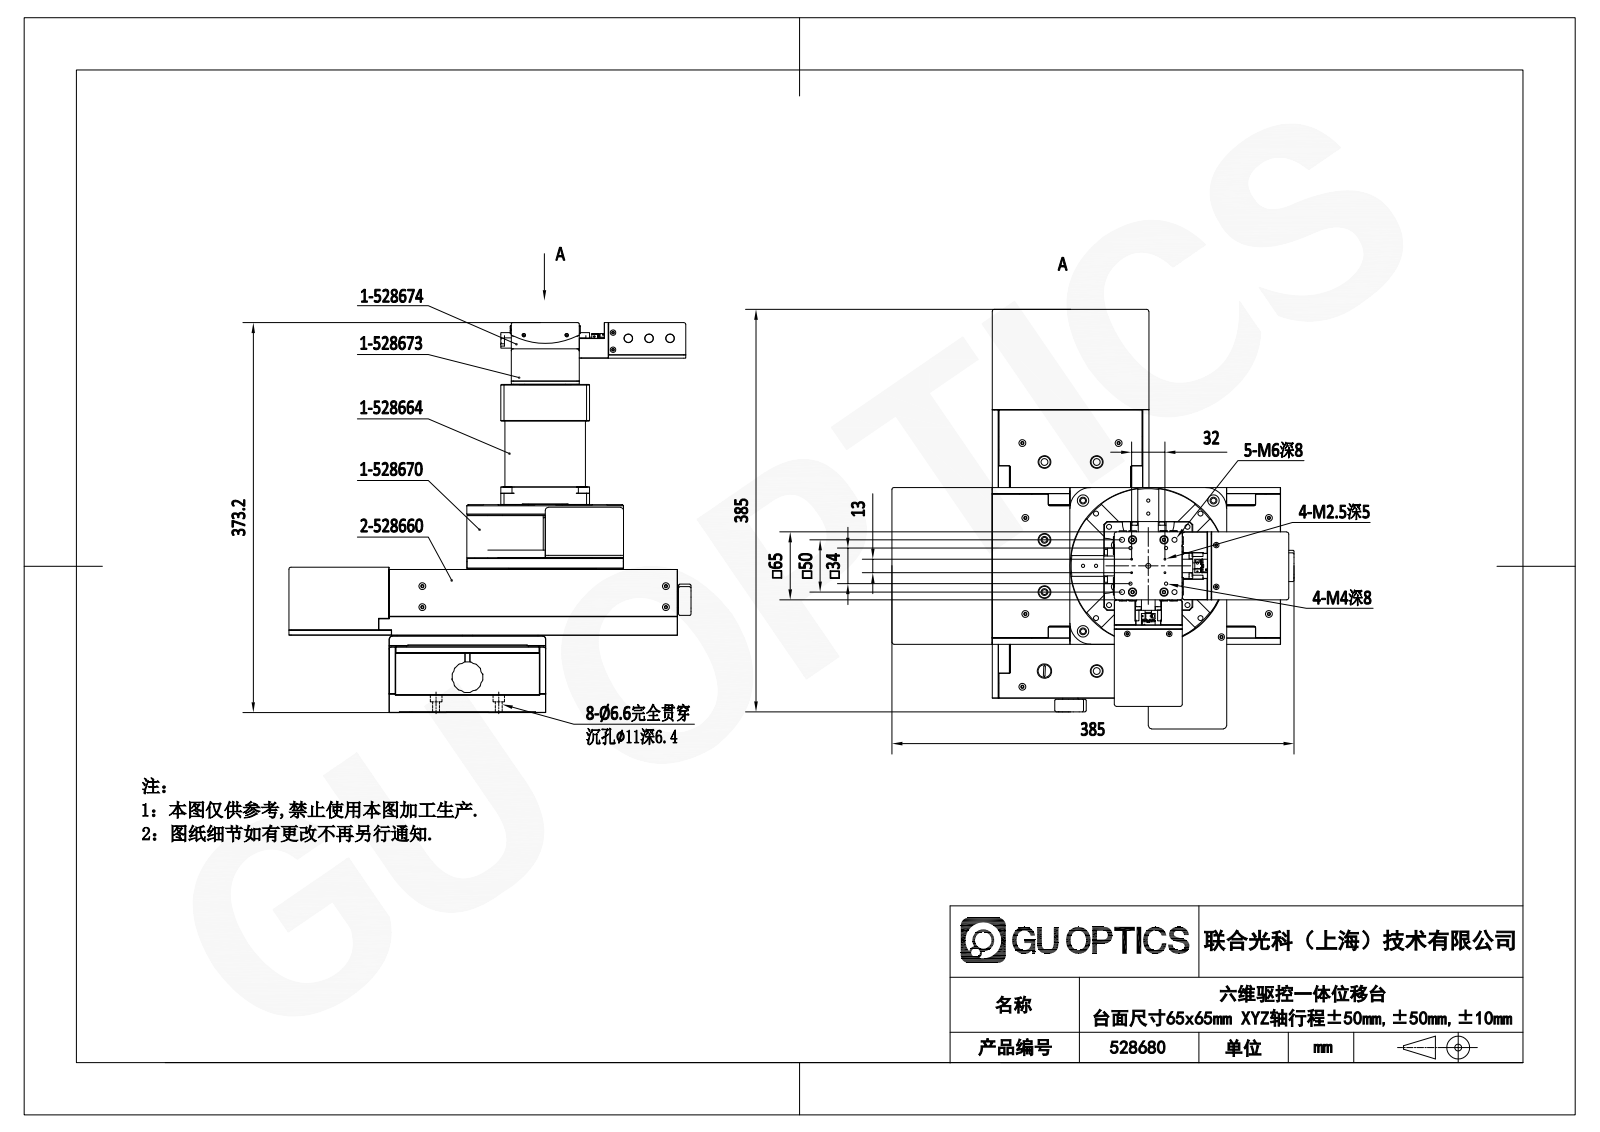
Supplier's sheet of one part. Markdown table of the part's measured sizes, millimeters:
| quantity | value |
| --- | --- |
| part name | 528673; 528670; 528674; 528660 (+2 more) |
| STEP written by | SolidWorks 2020 (CONFIG_CONTROL_DESIGN) |
| units | millimeters |
| bodies | 227 solids, 9631 faces (5832 planar, 2275 cylindrical, 1524 other) |
| overall size | 401.44 × 385 × 373.2 |
| volume | 6 316 000 mm³ |
| surface area | 1 927 000 mm² |
| round holes (diameter × count) | 2.5 × 114, 5 × 106, 3.3 × 93, 3.4 × 86, 6.5 × 73, 11 × 47, 6.6 × 43, 8 × 38, 4.5 × 36, 3.5 × 34, 2.05 × 30, 6 × 26 |
| round bosses / shafts (diameter × count) | 2 × 36, 4 × 20, 3 × 18, 7 × 16, 7.5 × 8, 5.5 × 8, 2.5 × 8, 2.4 × 8 |
| partial cylindrical surfaces (radius × count) | 2 × 153, 1 × 85, 5 × 57, 3 × 35, 4 × 19, 7.5 × 18, 2.5 × 13, 1.5 × 12 |
| main face-to-face distances | 74, 6, 56.5, 17.5, 16.5, 62.5, 39, 45, 40, 150 |
| hole center spacings | 20, 25, 32.02, 15, 50, 16, 30, 31 |
